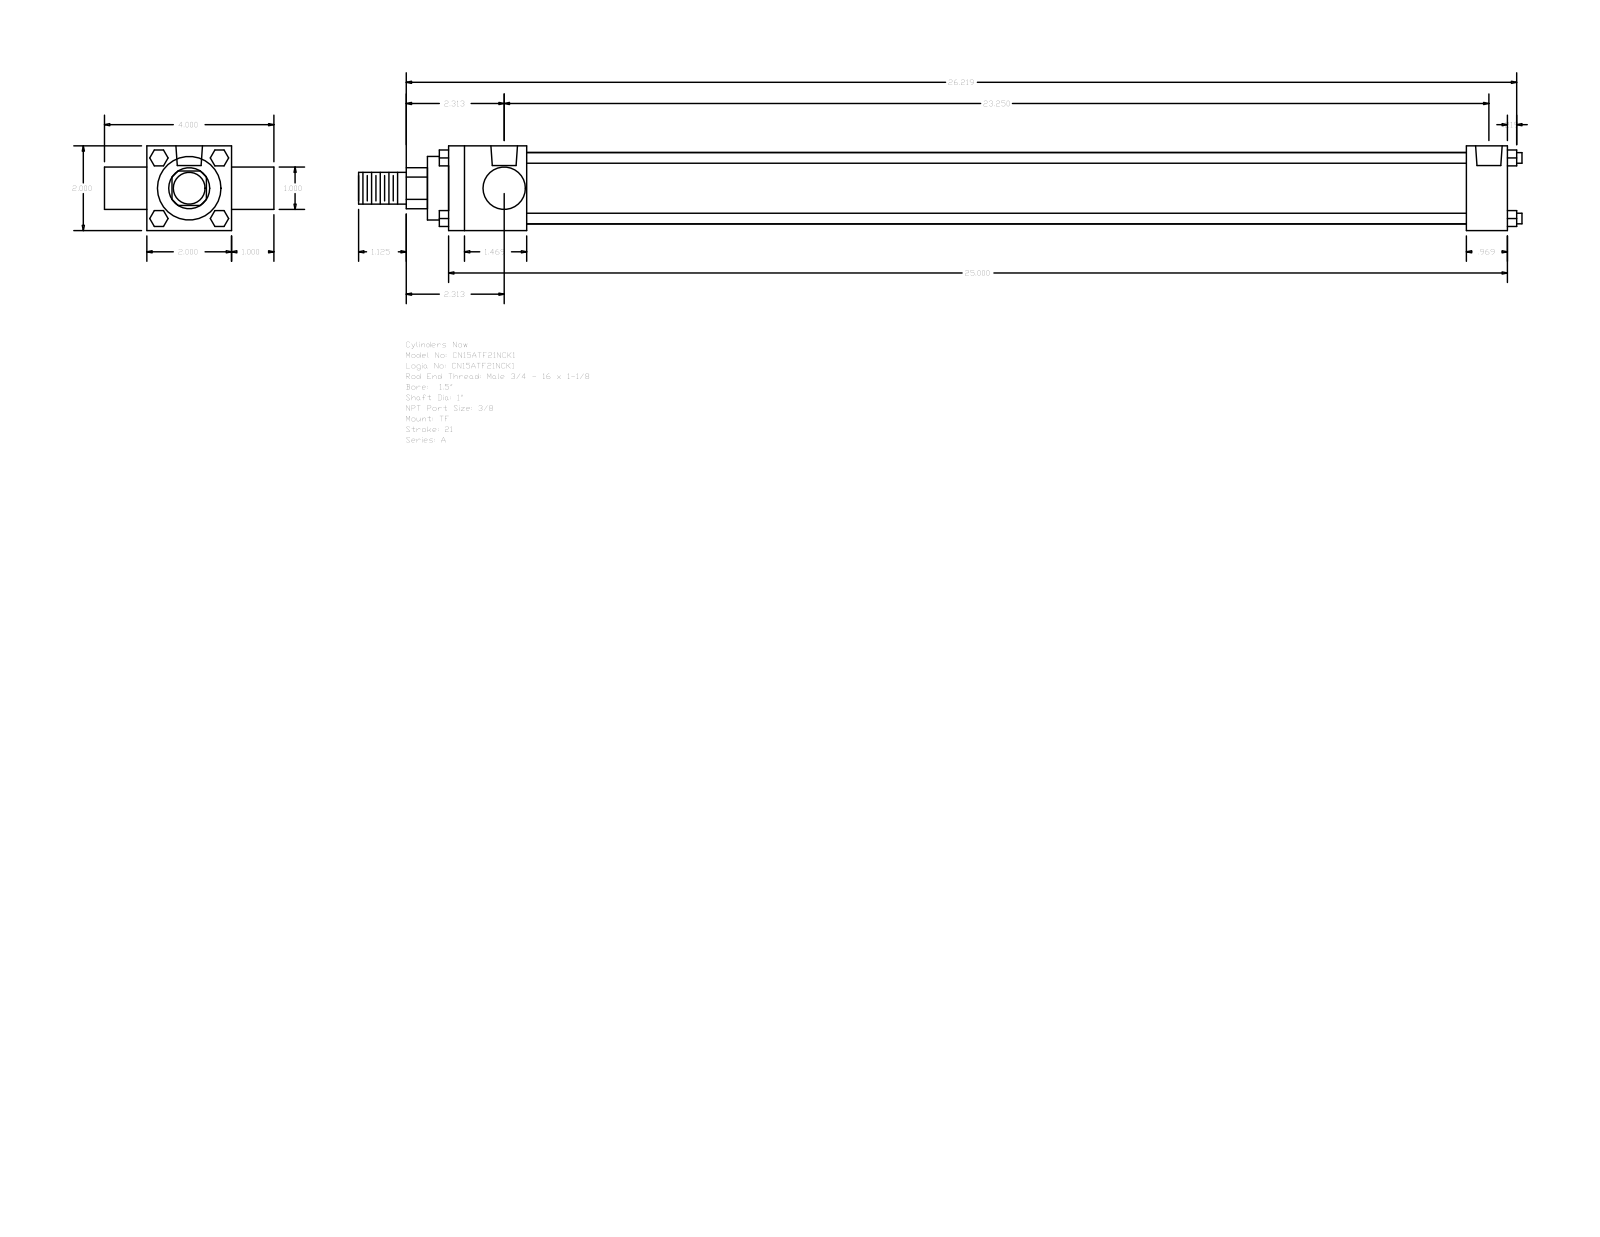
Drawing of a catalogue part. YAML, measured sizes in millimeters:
part_name: "A_TF__0150_1"
step_written_by: "GSSL Pune (CONFIG_CONTROL_DESIGN)"
units: millimeters
bodies: {solids: 0, faces: 120, planar: 92, cylindrical: 28, other: 0}
overall_size: [697.71, 101.6, 50.8]
round_holes:
  - {diameter: 5.56, count: 3}
  - {diameter: 15.93, count: 2}
round_bosses_or_shafts:
  - {diameter: 6.35, count: 4}
  - {diameter: 25.4, count: 2}
  - {diameter: 42.93, count: 1}
  - {diameter: 38.1, count: 1}
  - {diameter: 19.05, count: 1}
partial_cylinders:
  - {radius: 12.29, count: 1}
face_to_face_distances: [50.8, 25.4, 635, 76.2, 46.83, 610.39, 563.56, 588.17, 24.61, 12.7]
hole_center_spacings: [3.97, 586.58, 582.61, 590.55]
